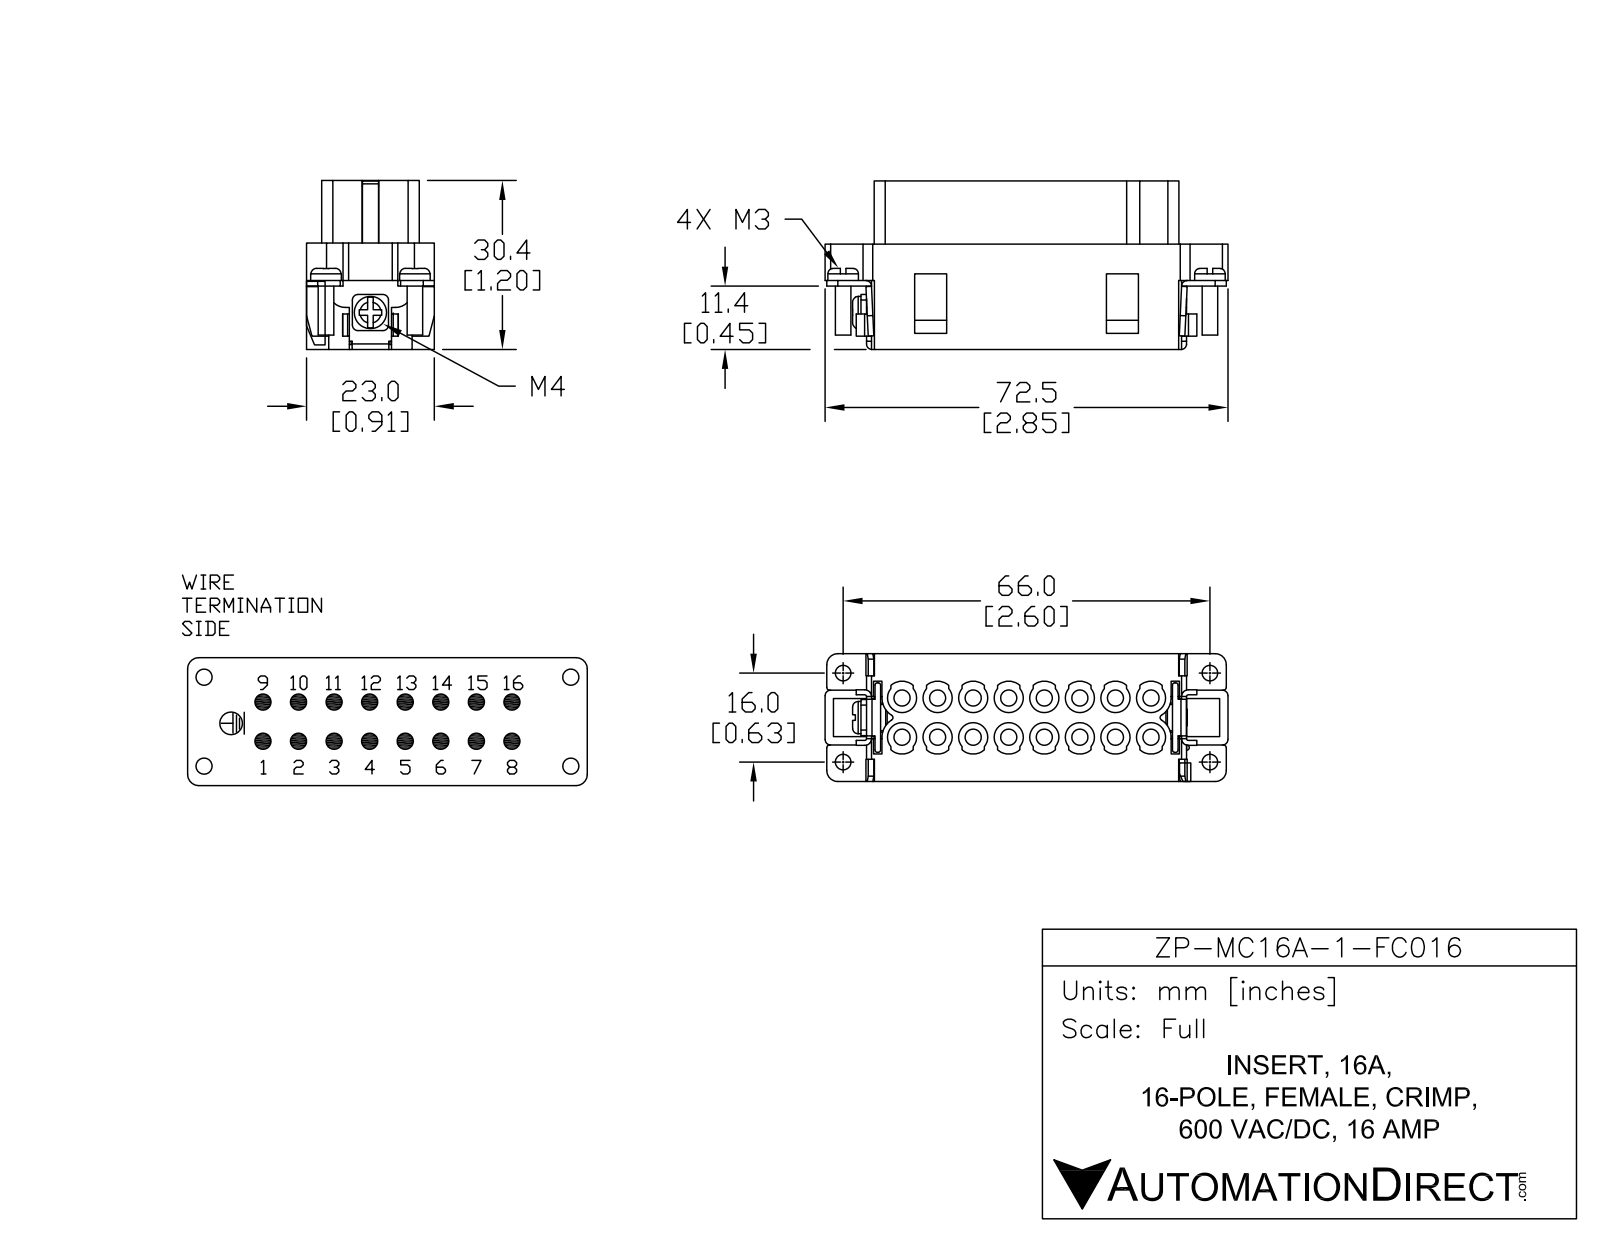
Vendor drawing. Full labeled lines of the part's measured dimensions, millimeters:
Part name (STEP PRODUCT): ZP-MC16A-1-FC016
STEP written by: SolidWorks 2014 (AUTOMOTIVE_DESIGN)
Units: millimetres
Bodies: 11 solids, 731 faces (464 planar, 257 cylindrical, 10 other)
Overall size (bounding box): 72.5 × 30.5 × 23
Volume: 27 293 mm³ · Surface area: 19 107 mm²
Round holes (diameter × count): ⌀2.9 ×16, ⌀2.15 ×7, ⌀2.85 ×1
Round bosses / shafts (diameter × count): ⌀4.9 ×12, ⌀5.5 ×4, ⌀2.8 ×4, ⌀5.8 ×1
Partial cylindrical surfaces — rounded edges, fillets, slot ends (radius × count): R0.25 ×28, R0.5 ×17, R2.62 ×16, R3.03 ×16, R1 ×12, R0.4 ×8, R0.75 ×8, R2 ×8
Main face-to-face distances: 23, 17.55, 2.72, 20.28, 19.25, 20.27, 2.73, 11.25, 30.5, 1
Hole centre spacings: 4.76, 10.22, 6.4, 16.38, 12.8, 22.67, 9.51, 19.2
